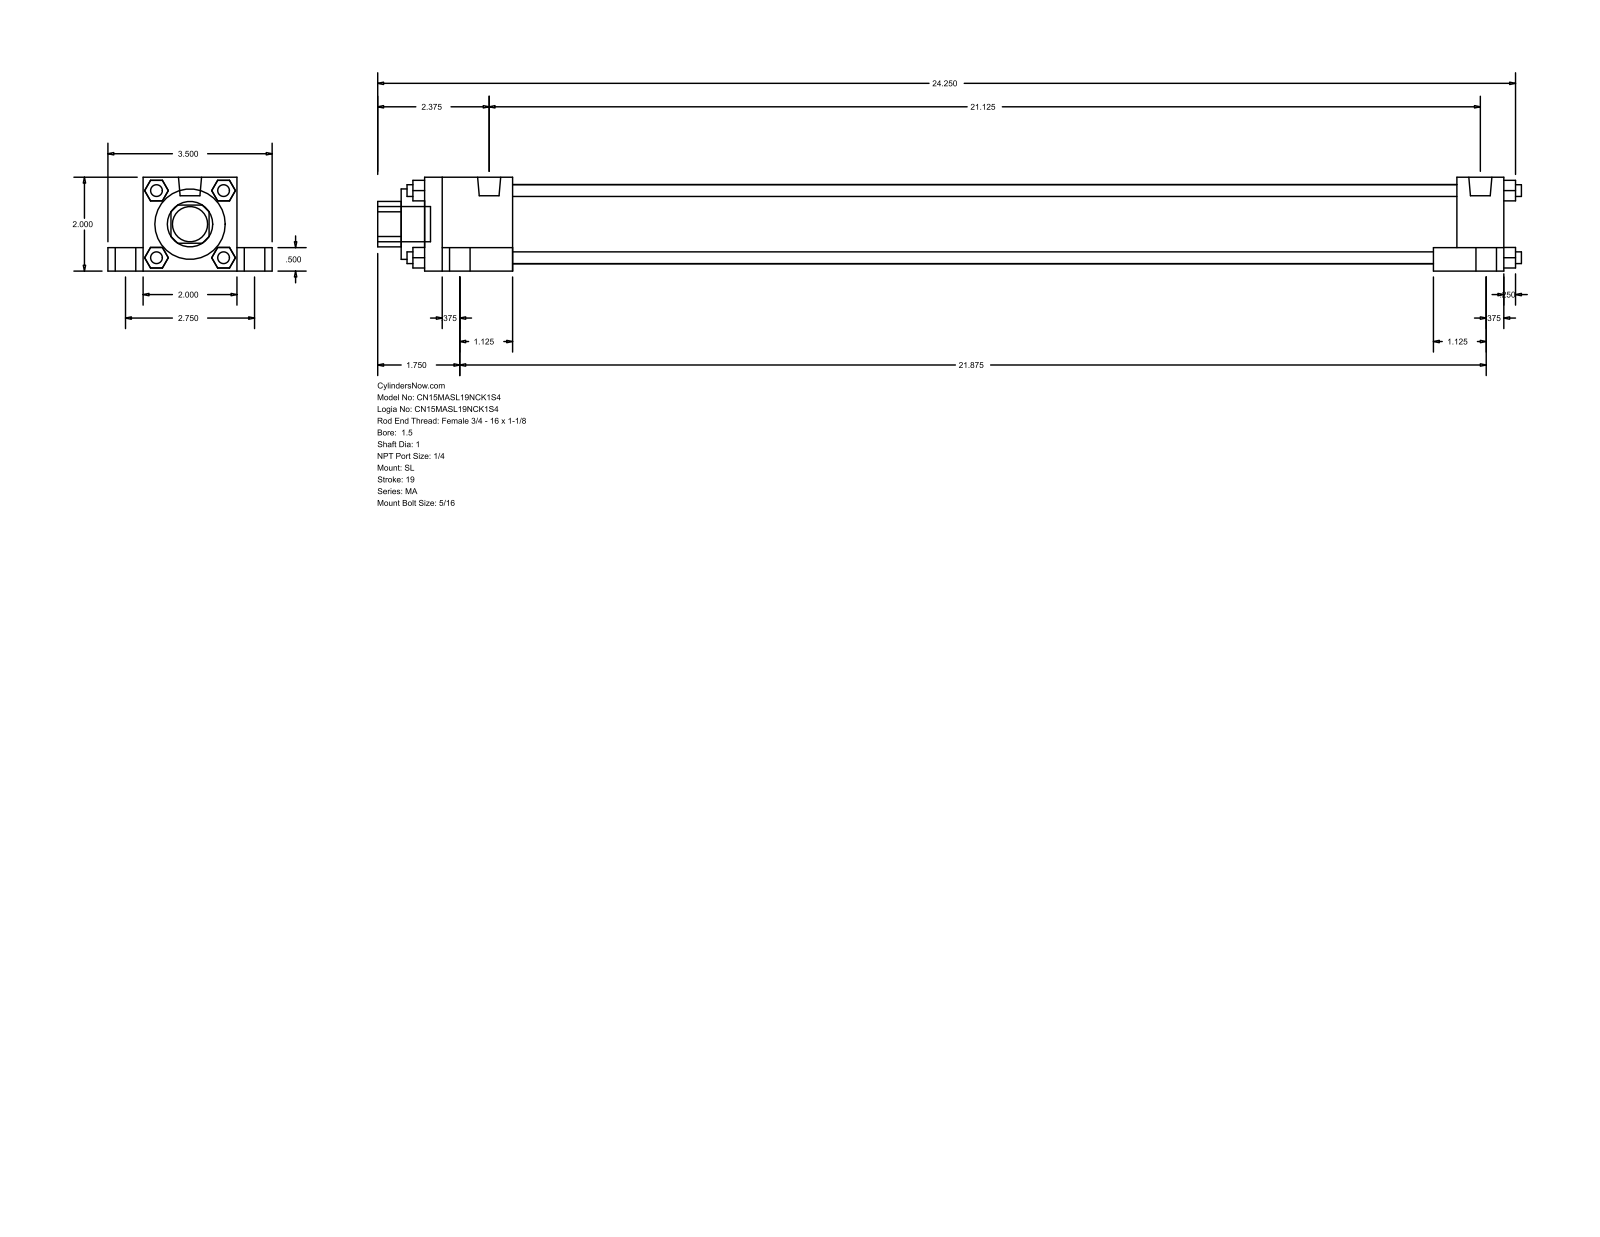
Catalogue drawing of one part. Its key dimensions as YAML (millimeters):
part_name: "MA_SL__0150_1"
step_written_by: "GSSL Pune (CONFIG_CONTROL_DESIGN)"
units: millimeters
bodies: {solids: 0, faces: 148, planar: 112, cylindrical: 36, other: 0}
overall_size: [619.12, 88.9, 50.8]
round_holes:
  - {diameter: 25.4, count: 1}
  - {diameter: 38.1, count: 1}
  - {diameter: 42.93, count: 1}
round_bosses_or_shafts:
  - {diameter: 17.46, count: 4}
  - {diameter: 11.11, count: 4}
  - {diameter: 7.94, count: 4}
  - {diameter: 6.35, count: 4}
  - {diameter: 12.49, count: 2}
  - {diameter: 19.05, count: 1}
partial_cylinders:
  - {radius: 12.29, count: 1}
face_to_face_distances: [50.8, 12.7, 19.05, 9.52, 69.85, 38.1, 6.35, 584.2, 25.4, 558.8]
